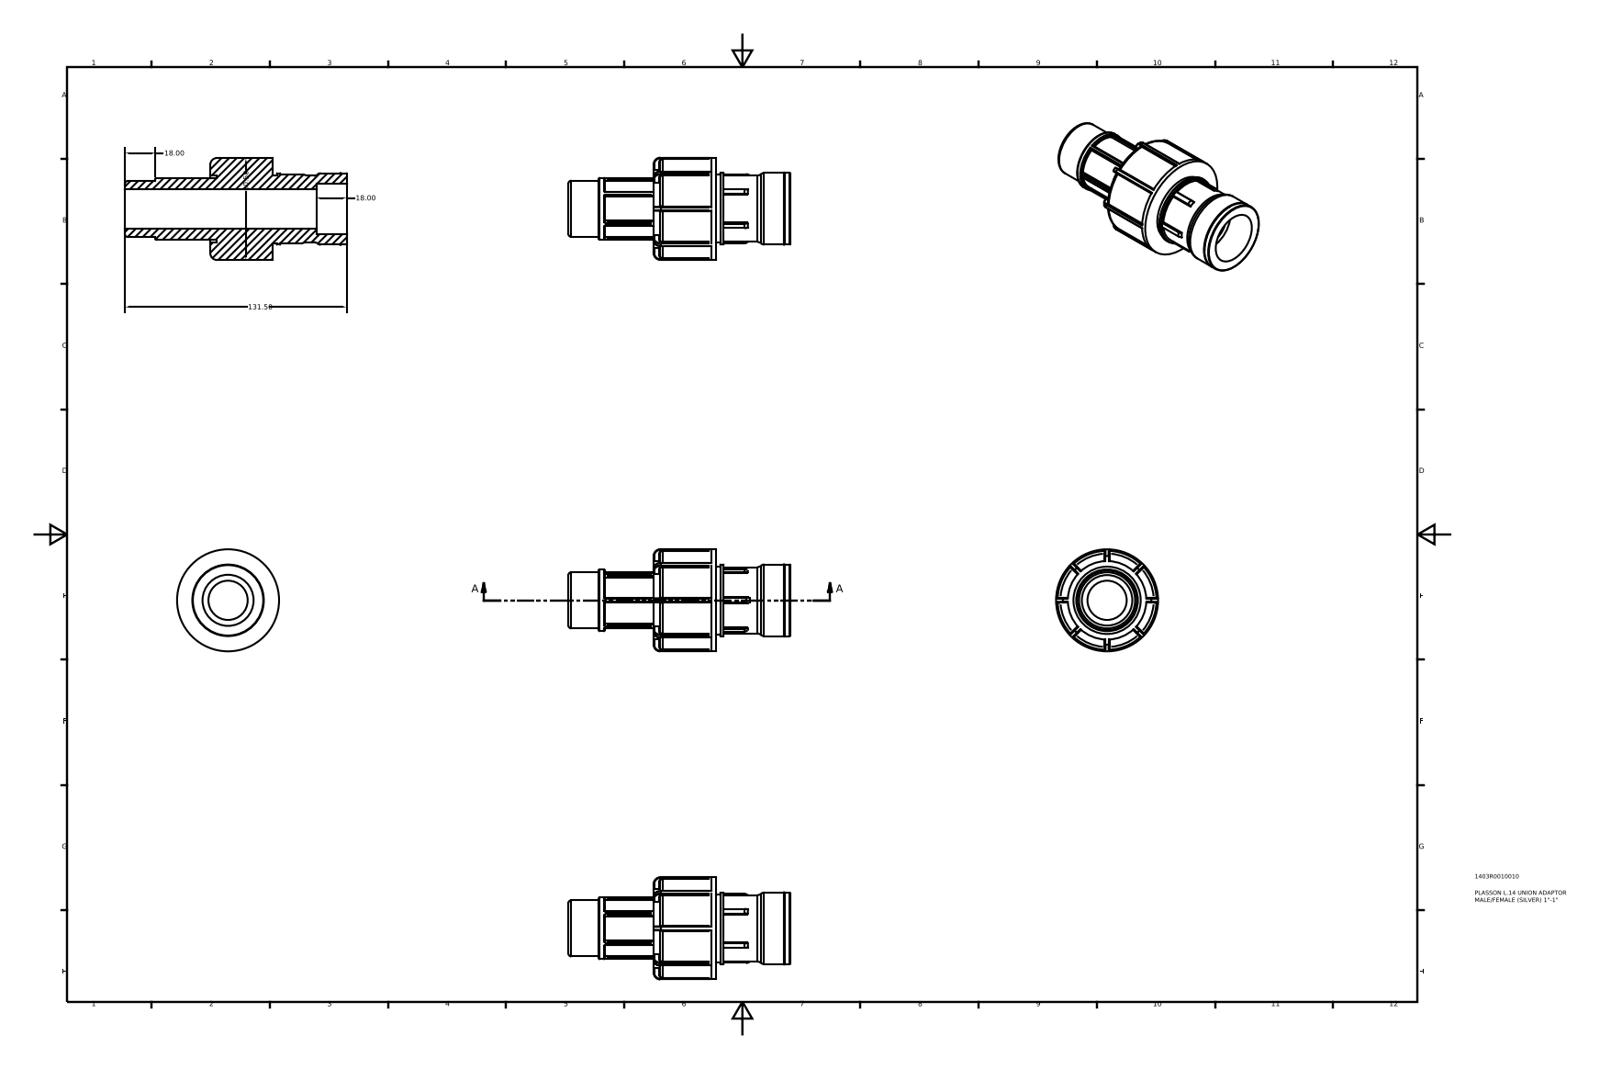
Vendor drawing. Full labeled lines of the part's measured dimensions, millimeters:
Part name (STEP PRODUCT): 1403R0010010
STEP written by: Autodesk Inventor 2015 (AUTOMOTIVE_DESIGN)
Units: millimetres
Bodies: 1 solid, 267 faces (77 planar, 126 cylindrical, 64 other)
Overall size (bounding box): 131.5 × 60.5 × 60.5
Volume: 137 765 mm³ · Surface area: 35 201 mm²
Round holes (diameter × count): ⌀23.27 ×1, ⌀30.29 ×1, ⌀39.9 ×1
Round bosses / shafts (diameter × count): ⌀60.5 ×1, ⌀58.69 ×1, ⌀46.55 ×1, ⌀42.41 ×1, ⌀40.29 ×1, ⌀39.38 ×1, ⌀36.57 ×1, ⌀33.25 ×1
Partial cylindrical surfaces — rounded edges, fillets, slot ends (radius × count): R0.3 ×54, R0.3 ×12, R0.67 ×12, R3.02 ×5
Main face-to-face distances: 33.22, 77.27, 44.05, 3.6, 36.82, 80.87, 18, 113.5, 62.87, 59.27
